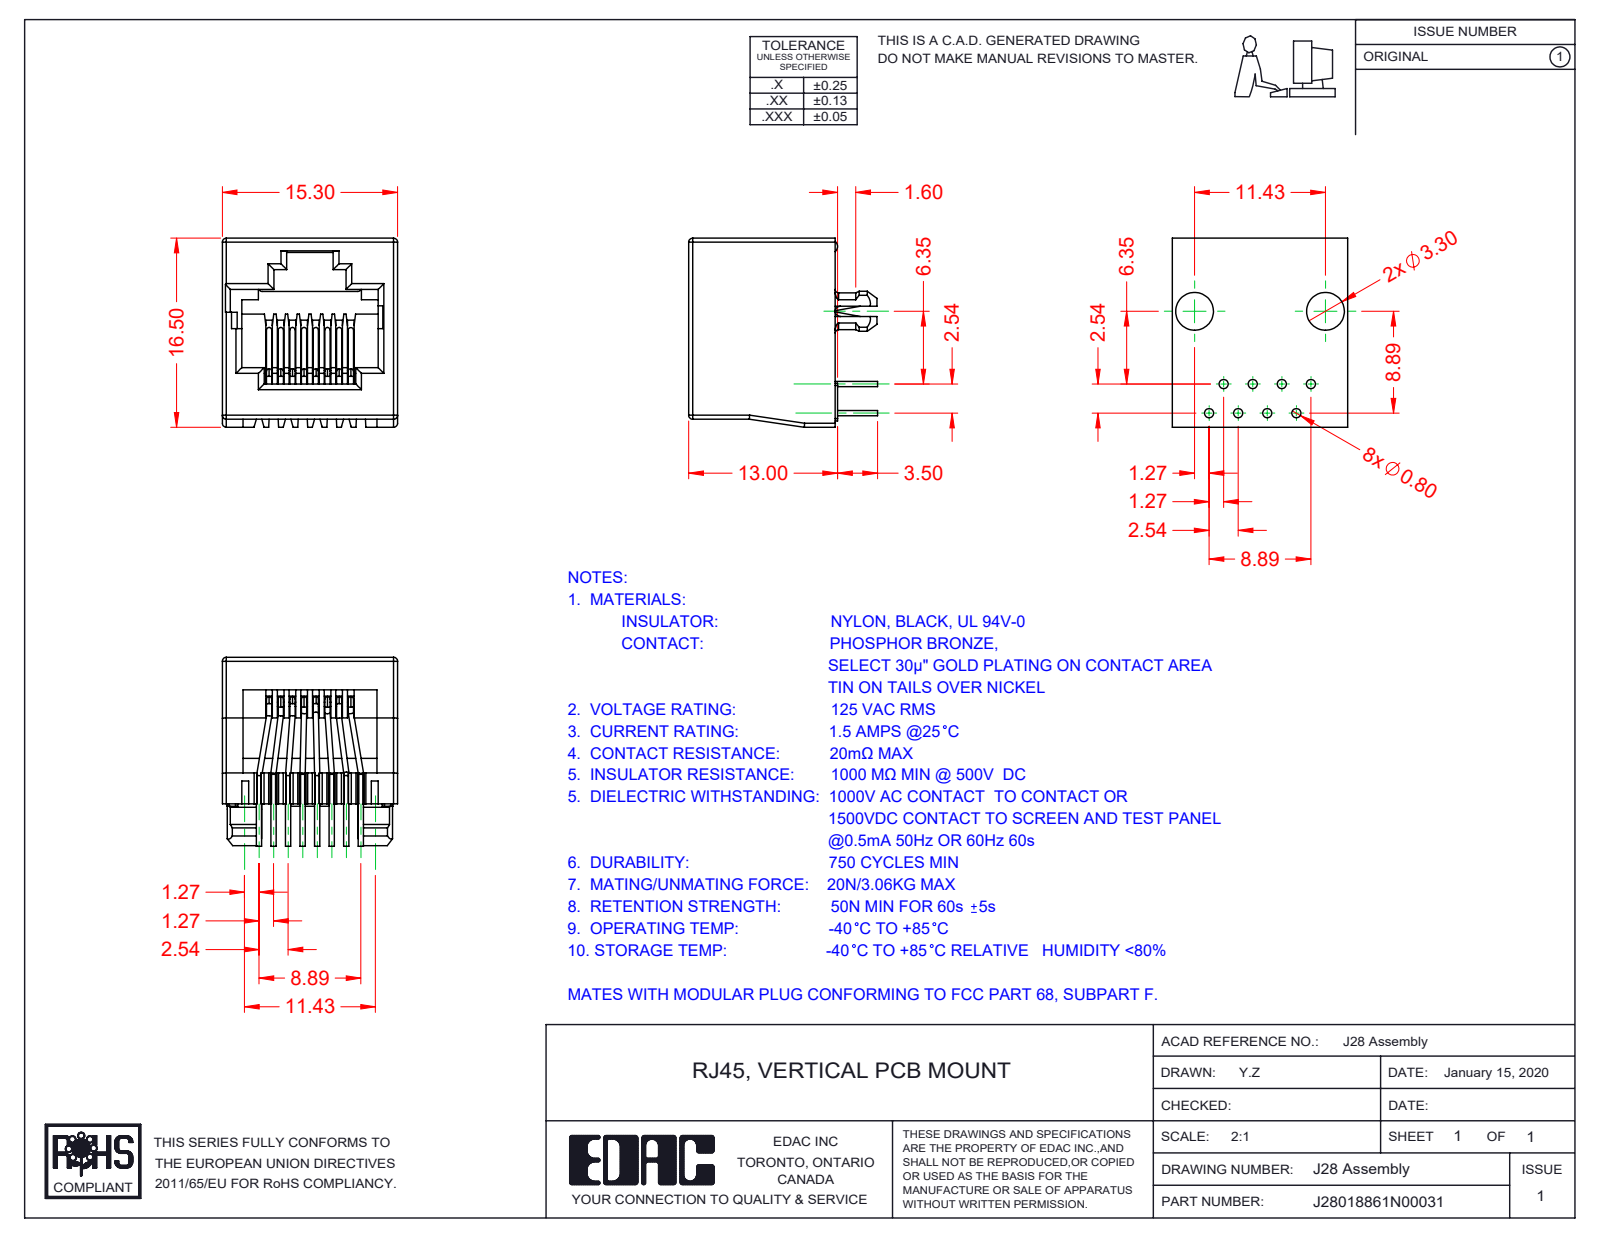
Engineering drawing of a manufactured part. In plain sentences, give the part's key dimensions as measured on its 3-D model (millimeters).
The part is named "28 Contacts; 28 Insulator; RJ28018861N00031". Its 3-D file was written by "SolidWorks 2016 (CONFIG_CONTROL_DESIGN)". It is 9 solids with 580 faces: 319 planar, 205 cylindrical and 56 other. Overall it measures 16.5 by 16.5 by 15.3 millimeters. Its volume is 1 535 cubic millimeters and its surface area 2 745 square millimeters. Round holes: 2 of diameter 1.6. Round bosses or shafts: 45 of diameter 0.46. Partial cylindrical surfaces (rounded edges, fillets, slot ends): 19 of radius 0.5, 16 of radius 0.1, 14 of radius 0.35, 10 of radius 0.25, 8 of radius 0.2, 8 of radius 0.23, 2 of radius 0.45, 2 of radius 1.6. The main face-to-face distances are 15.3, 1.02, 1.7, 13.6, 1.25, 2.04, 12.81, 3.06, 3.15, 12.15. The hole center spacings are 12.
